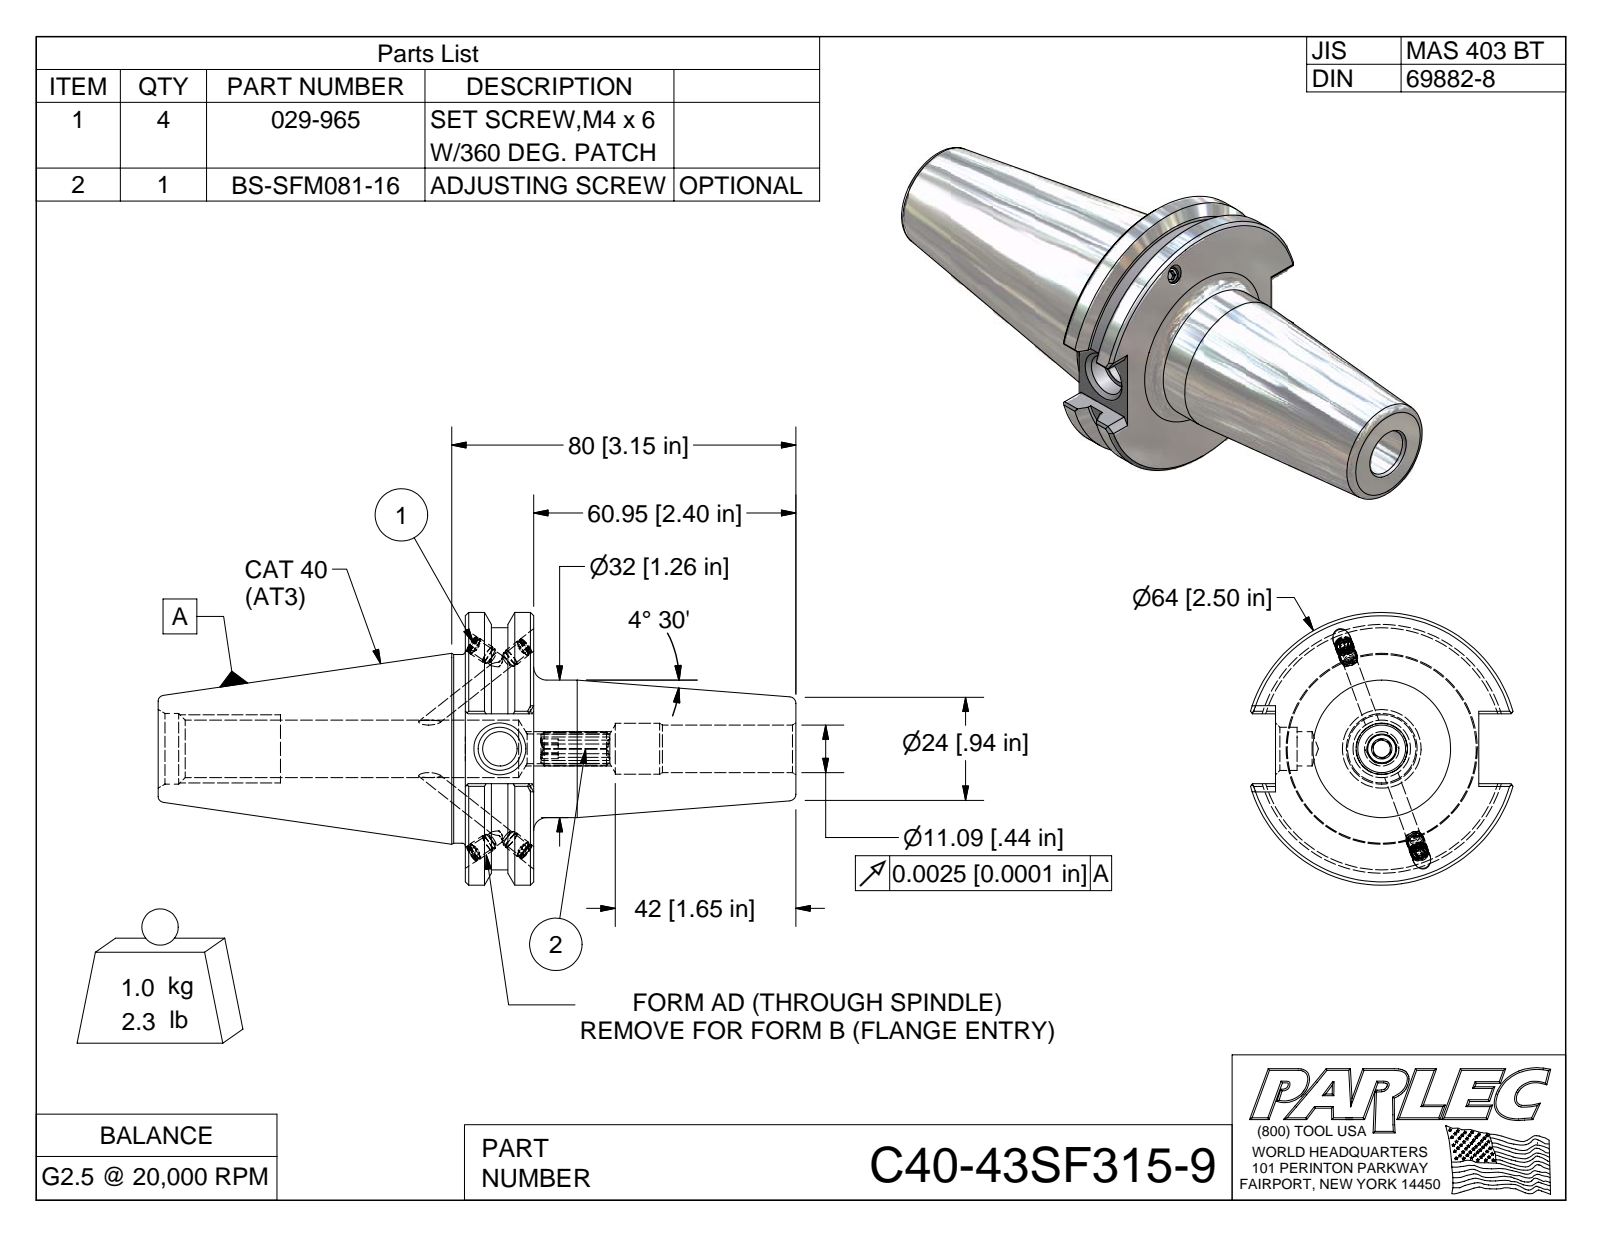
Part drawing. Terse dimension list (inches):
name: C40-43SF315-9; C40BC-43SF315-9-1; 029-965; BS-SFM081-16
written by: Autodesk Inventor 2009 (AUTOMOTIVE_DESIGN)
unit: in
bodies: 6 solids, 172 faces (87 planar, 32 cylindrical, 53 other)
size: 5.837 × 2.5 × 2.403
volume: 8.271 in³; area: 45 in²
holes: 4× ⌀0.13, 4× ⌀0.161, 1× ⌀0.437, 1× ⌀0.467
bosses: 4× ⌀0.165, 4× ⌀0.157, 1× ⌀2.5, 1× ⌀2.219, 1× ⌀1.73, 1× ⌀1.26
rounds: 1× R0.157
face distances: 0.625, 3.025, 2.4, 0.64, 1.86, 2.812, 3.437, 5.837, 3.201, 0.389
